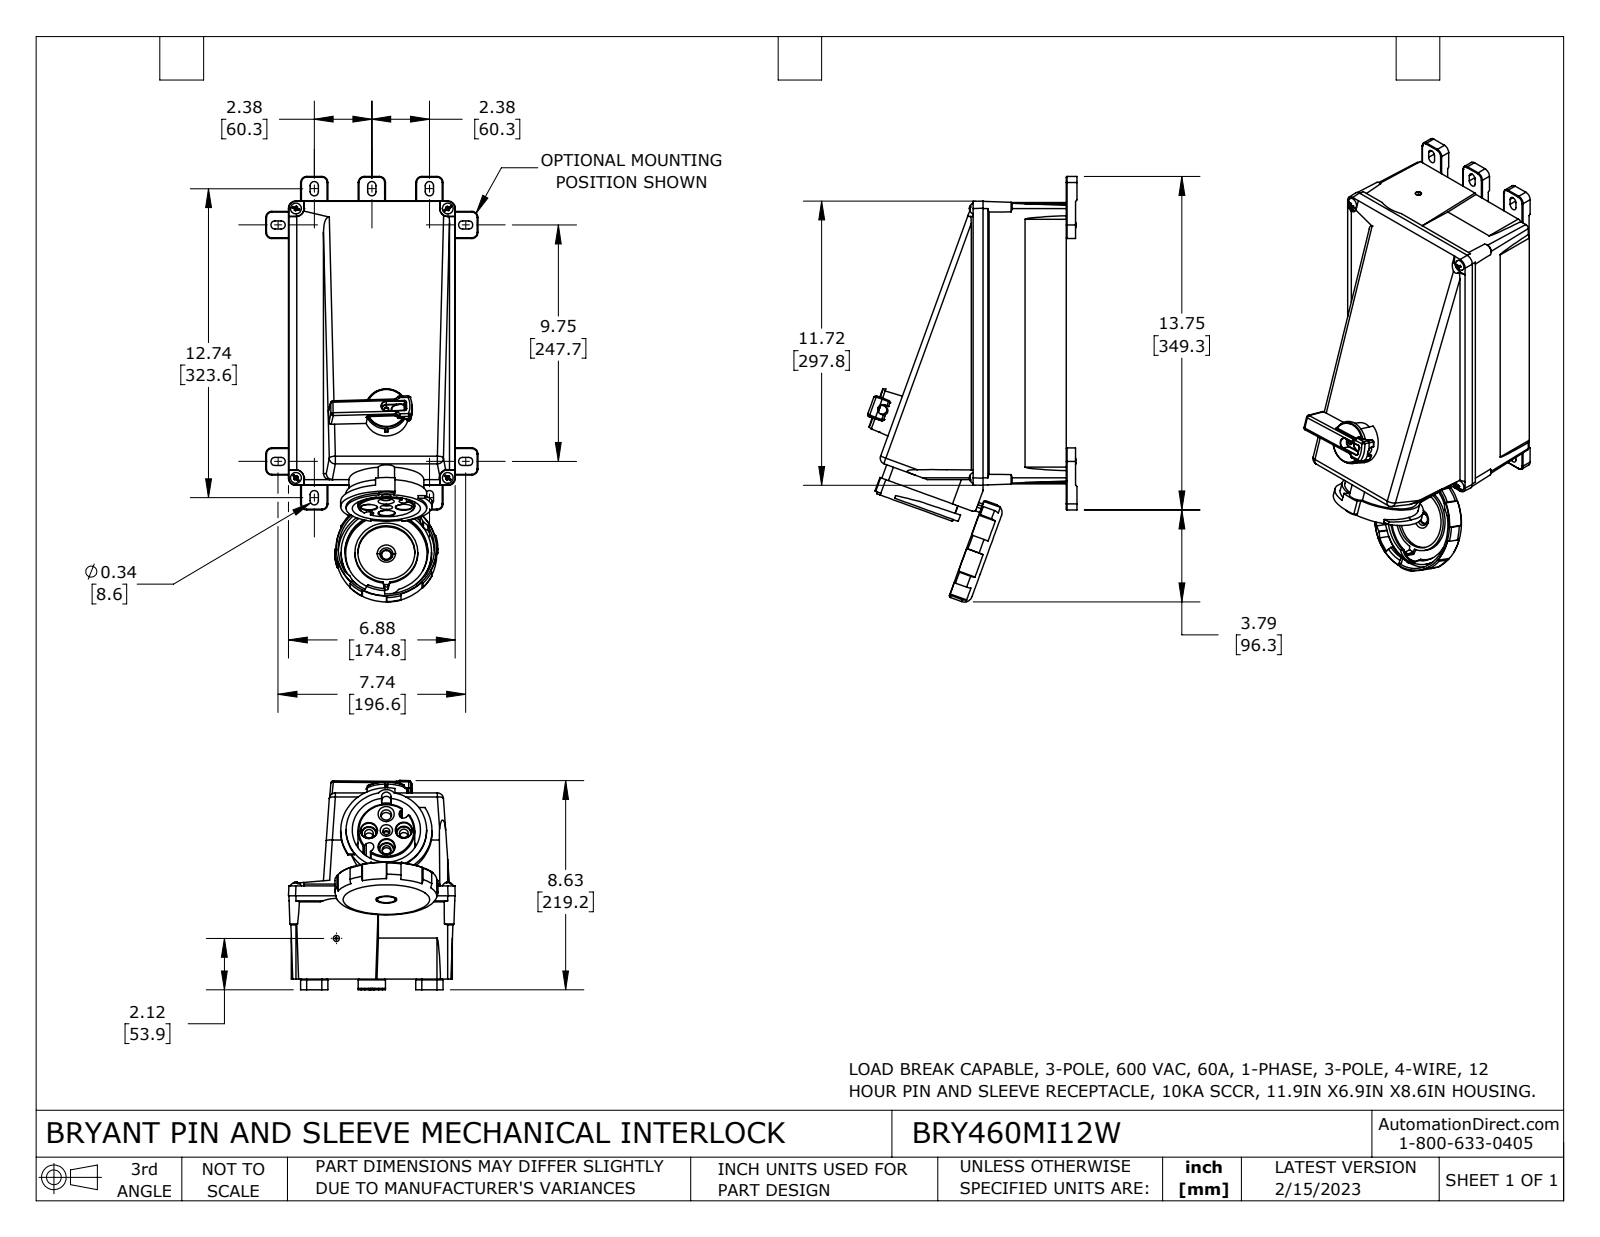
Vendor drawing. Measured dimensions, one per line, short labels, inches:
name: BRY460MI12W
written by: SolidWorks 2021 (CONFIG_CONTROL_DESIGN)
unit: in
bodies: 21 solids, 2559 faces (920 planar, 879 cylindrical, 760 other)
size: 17.549 × 8.75 × 8.635
volume: 429.3 in³; area: 864.7 in²
holes: 5× ⌀0.281, 3× ⌀0.12, 3× ⌀0.366, 2× ⌀0.101, 2× ⌀0.157, 2× ⌀0.25, 1× ⌀0.125, 1× ⌀0.125, 1× ⌀0.169, 1× ⌀0.19, 1× ⌀0.27, 1× ⌀0.28
bosses: 5× ⌀0.433, 4× ⌀1.12, 2× ⌀0.263, 1× ⌀3.73, 1× ⌀3.323, 1× ⌀3.091, 1× ⌀2.592, 1× ⌀2.342
rounds: 135× R0.015, 54× R0.08, 47× R0.03, 24× R0.02, 24× R0.25, 20× R0.075, 19× R0.09, 18× R0.17
face distances: 3.44, 6.646, 0.12, 0.15, 11.594, 5.528, 0.14, 5.388, 6.818, 5.363
hole spacings: 1.595, 0.71, 1.016, 0.59, 0.59, 0.71, 1.42, 4.172
